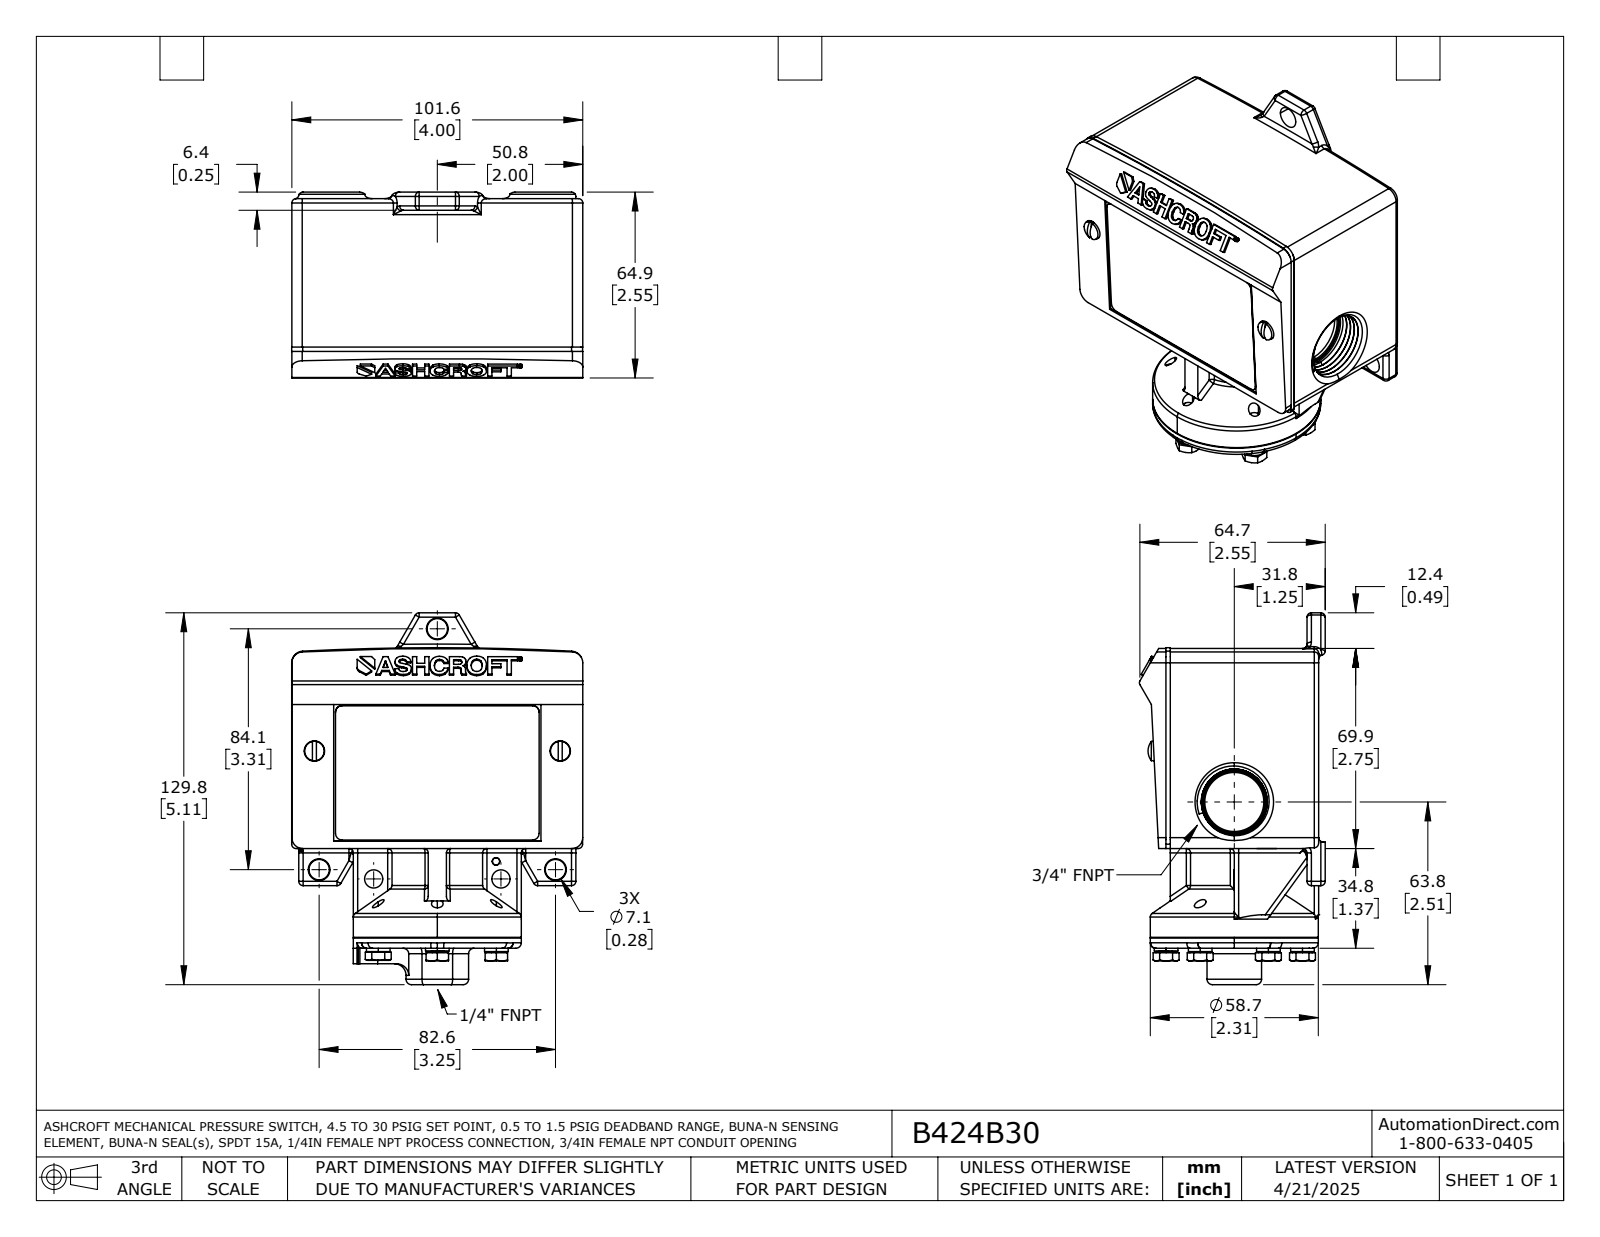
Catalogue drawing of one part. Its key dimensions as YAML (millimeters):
part_name: "B424B30"
step_written_by: "SolidWorks 2021 (AUTOMOTIVE_DESIGN)"
units: millimeters
bodies: {solids: 2, faces: 1259, planar: 345, cylindrical: 472, other: 442}
overall_size: [129.8, 101.7, 64.9]
volume: 468200
surface_area: 54520
round_holes:
  - {diameter: 4.1, count: 6}
  - {diameter: 4.9, count: 5}
  - {diameter: 5.3, count: 5}
  - {diameter: 4.7, count: 4}
  - {diameter: 7.1, count: 2}
  - {diameter: 11.6, count: 1}
  - {diameter: 20.6, count: 1}
round_bosses_or_shafts:
  - {diameter: 8.3, count: 6}
  - {diameter: 7.1, count: 6}
  - {diameter: 4.8, count: 5}
  - {diameter: 6.9, count: 2}
  - {diameter: 6.4, count: 2}
  - {diameter: 58.7, count: 1}
partial_cylinders:
  - {radius: 1.5, count: 92}
  - {radius: 0.8, count: 5}
  - {radius: 1.9, count: 4}
  - {radius: 2.3, count: 4}
  - {radius: 3.8, count: 4}
  - {radius: 0.3, count: 2}
  - {radius: 2.4, count: 2}
  - {radius: 4.1, count: 2}
face_to_face_distances: [101.6, 0.4, 34.8, 2.3, 99.3, 11.2, 90.4, 88.1, 8.9, 21.5]
hole_center_spacings: [23.8, 41.2, 47.6, 23.8, 85.9]
